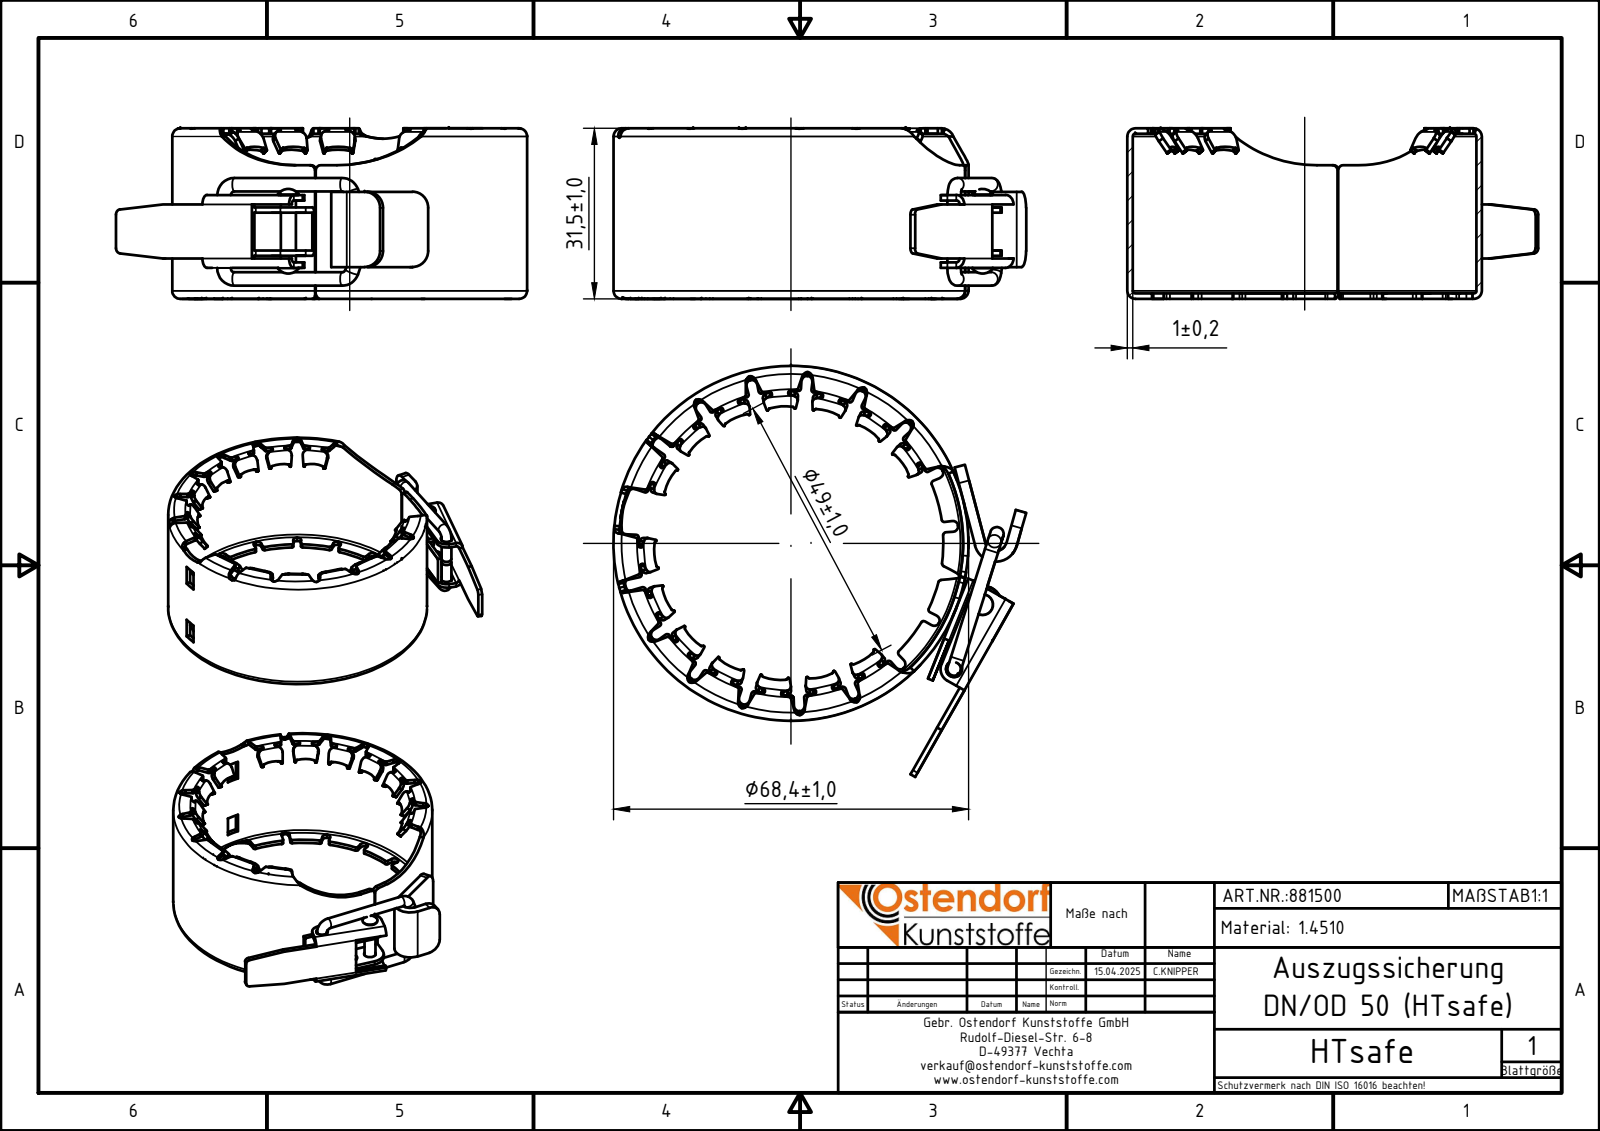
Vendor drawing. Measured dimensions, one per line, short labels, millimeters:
name: 881500z
written by: Autodesk Inventor 2024 (AUTOMOTIVE_DESIGN)
unit: mm
bodies: 6 solids, 972 faces (126 planar, 65 cylindrical, 781 other)
size: 76.61 × 76.33 × 31.66
volume: 9 418 mm³; area: 19 120 mm²
holes: 3× ⌀3, 1× ⌀63.89
bosses: 3× ⌀2.5, 1× ⌀65.89, 1× ⌀2.8
rounds: 12× R1.95, 5× R3, 4× R1, 2× R0.74, 2× R1.74, 2× R3.5, 1× R1.95, 1× R1.95
face distances: 1, 2, 8, 12.42, 24.9, 12.48, 10.23, 2.25, 14.67, 2.23
hole spacings: 5.01, 8.05, 13.06, 37.16, 37.4, 38.23
